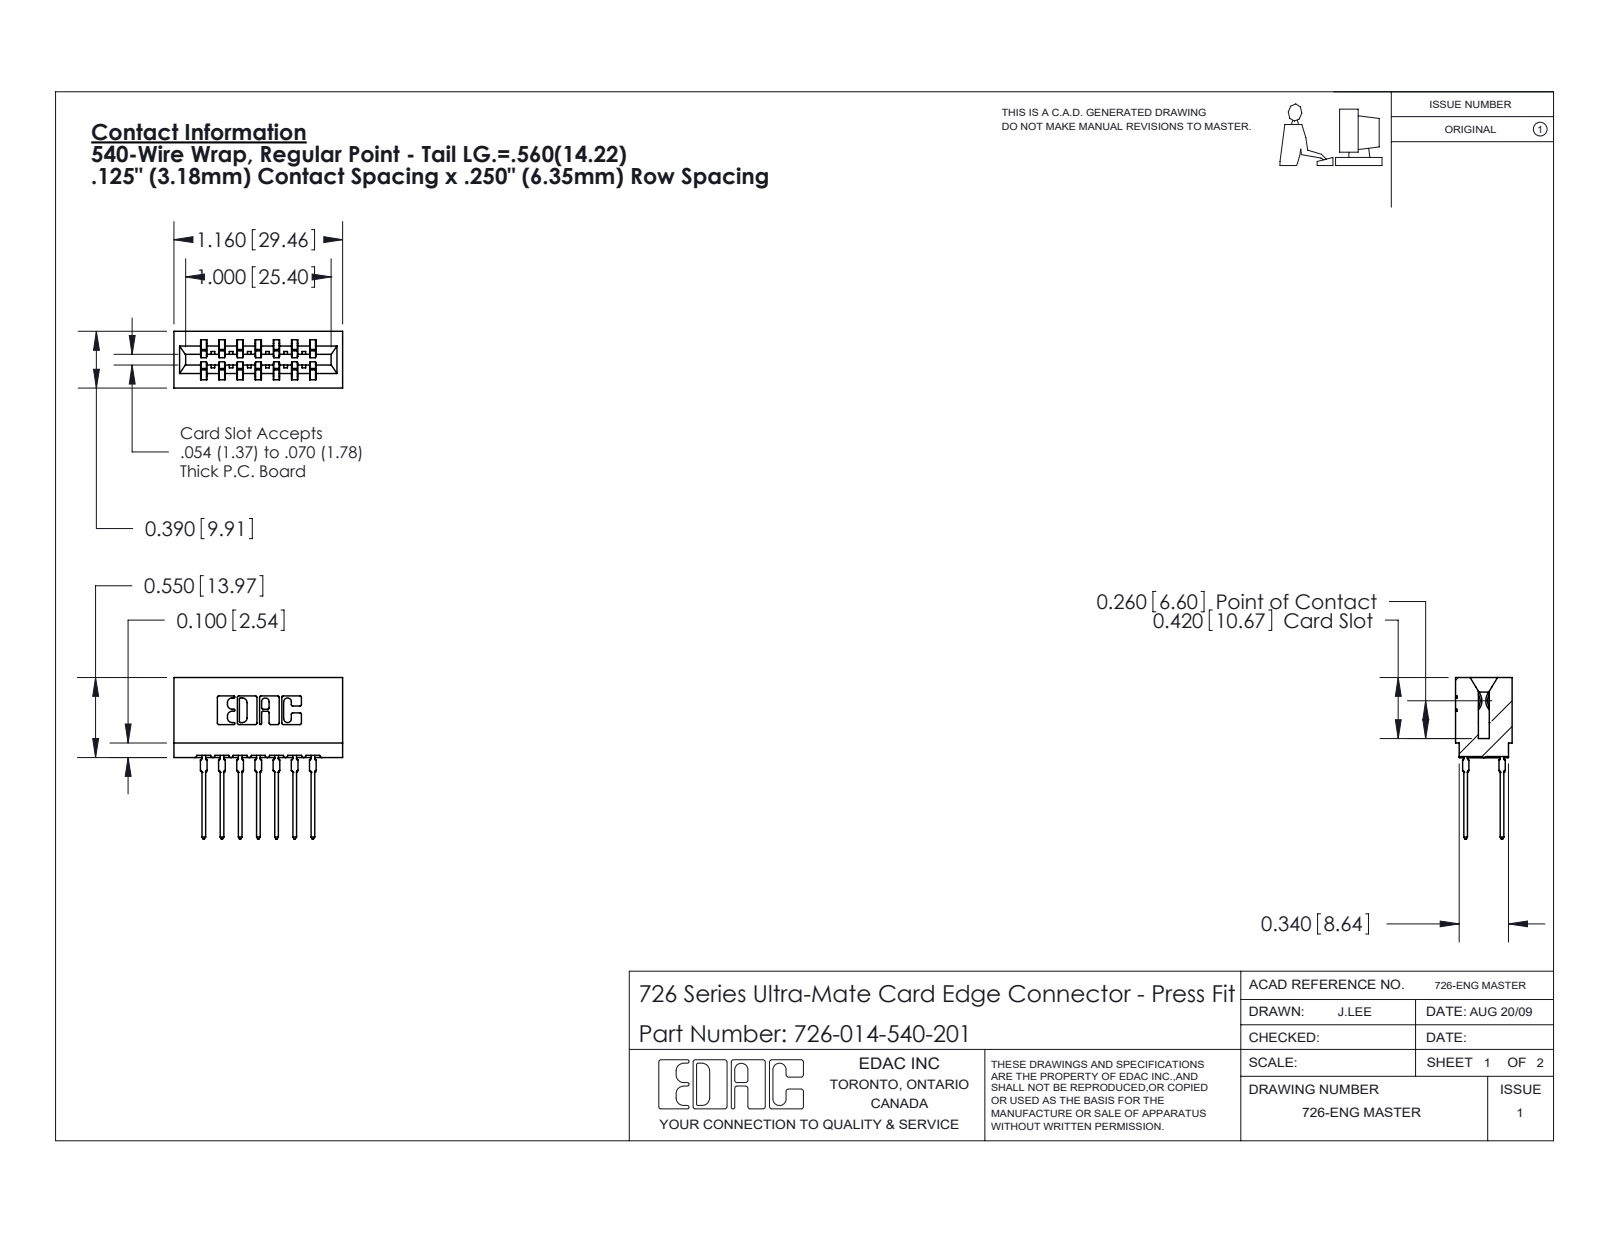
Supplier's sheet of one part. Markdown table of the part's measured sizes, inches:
| quantity | value |
| --- | --- |
| part name | 746-292-001_540; 726-014-540-201; 726 Part_.515 Slot Depth - 01 |
| STEP written by | SolidWorks 2020 (CONFIG_CONTROL_DESIGN) |
| units | inches |
| bodies | 15 solids, 1350 faces (699 planar, 287 cylindrical, 364 other) |
| overall size | 1.16 × 1.109 × 0.39 |
| volume | 0.179 in³ |
| surface area | 6.934 in² |
| partial cylindrical surfaces (radius × count) | 0.021 × 28, 0.01 × 22, 0.005 × 8, 0.011 × 8, 0.015 × 8, 0.007 × 6, 0.031 × 6, 0.026 × 3 |
| main face-to-face distances | 0.25, 0.057, 0.333, 0.042, 0.125, 0.125, 0.083, 0.5, 0.025, 0.307 |
